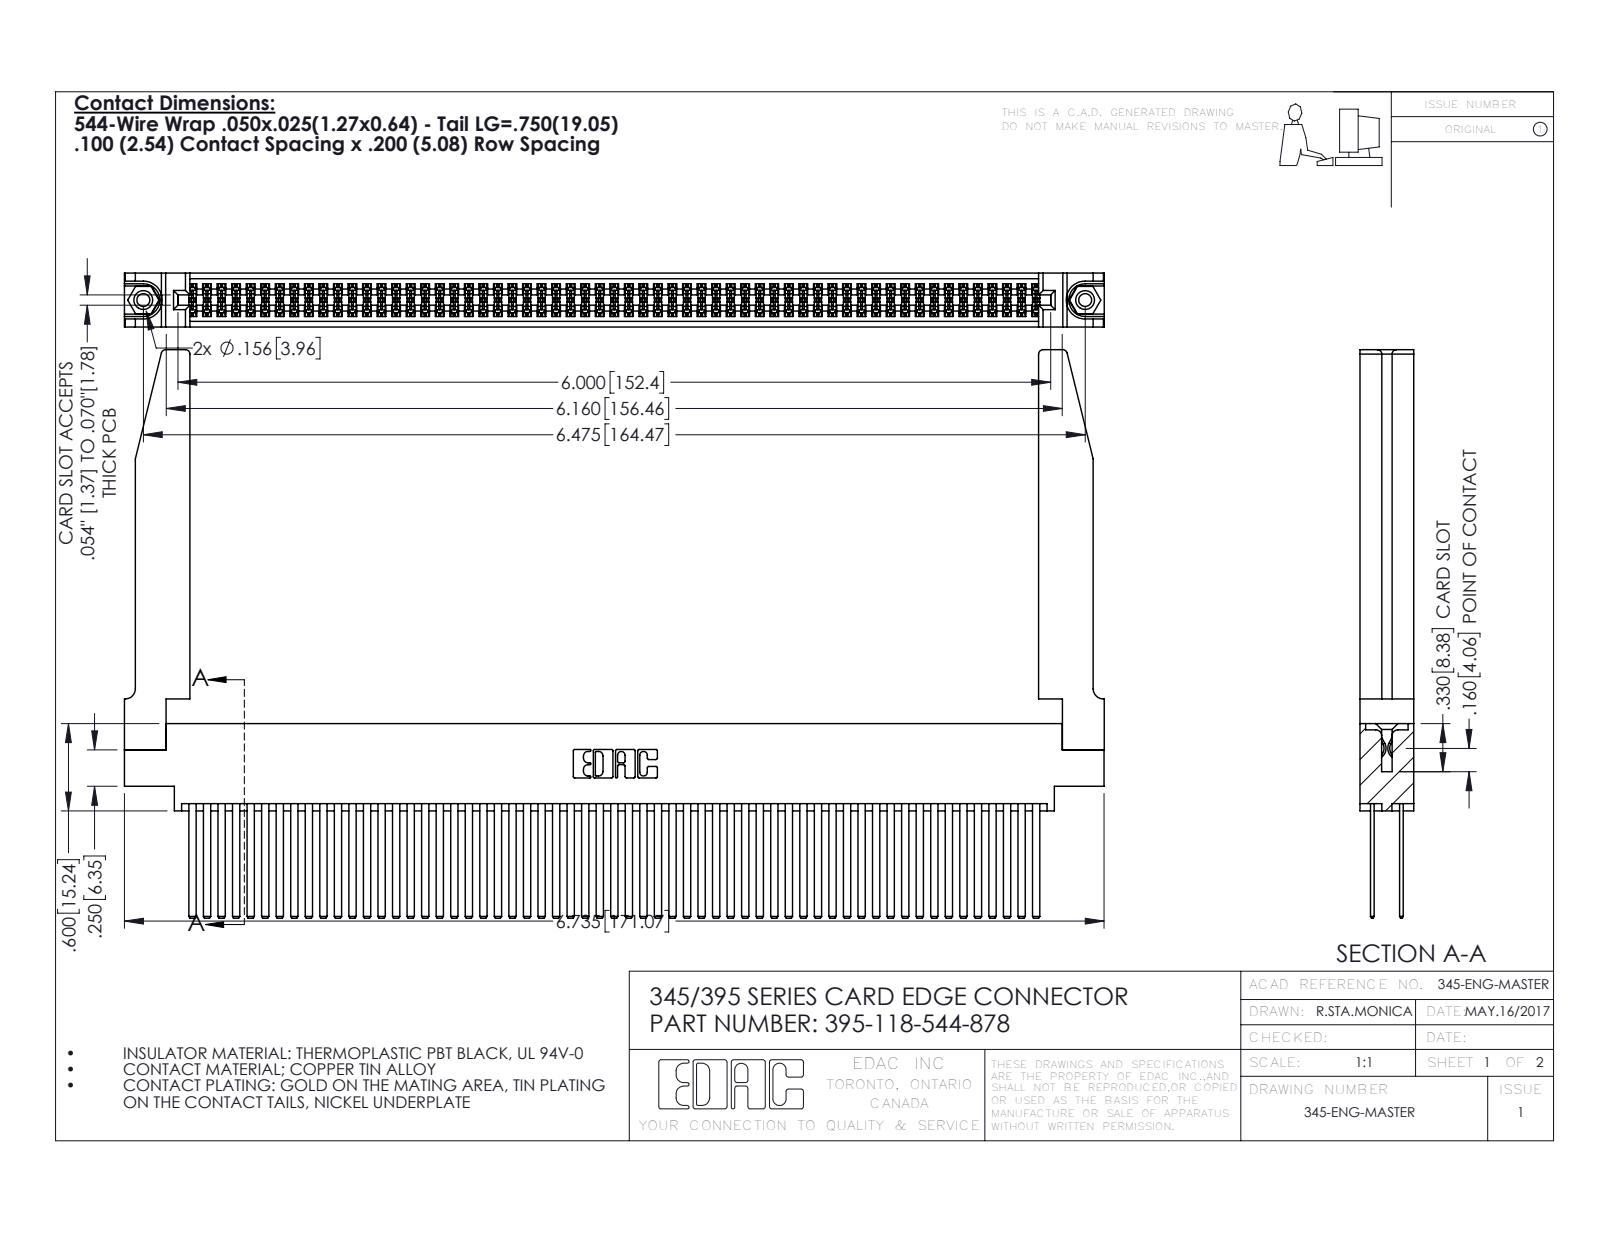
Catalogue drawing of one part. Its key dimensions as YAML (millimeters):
part_name: "395-118-544-878; 345-250-001_345-250-001-102; 345-292-001_345-293-144; 345 Part_0.170 Offset - 0.156 Dia-TH (+1 more)"
step_written_by: "SolidWorks 2016 (CONFIG_CONTROL_DESIGN)"
units: millimeters
bodies: {solids: 123, faces: 5556, planar: 3648, cylindrical: 1856, other: 52}
overall_size: [171.1, 99.2, 9.4]
volume: 26090
surface_area: 39240
round_holes:
  - {diameter: 2.3, count: 2}
  - {diameter: 3.2, count: 2}
  - {diameter: 4, count: 2}
  - {diameter: 1.6, count: 1}
round_bosses_or_shafts:
  - {diameter: 3.9, count: 2}
partial_cylinders:
  - {radius: 0.2, count: 177}
  - {radius: 0.3, count: 22}
  - {radius: 0.8, count: 8}
  - {radius: 0.2, count: 6}
  - {radius: 0.8, count: 6}
  - {radius: 0.7, count: 3}
  - {radius: 0.4, count: 2}
  - {radius: 0.5, count: 2}
face_to_face_distances: [1.8, 7.6, 2.5, 6.9, 0.6, 5.1, 9.4, 5.7, 4.4, 3.8]
hole_center_spacings: [6.9, 158.5, 164.5]
